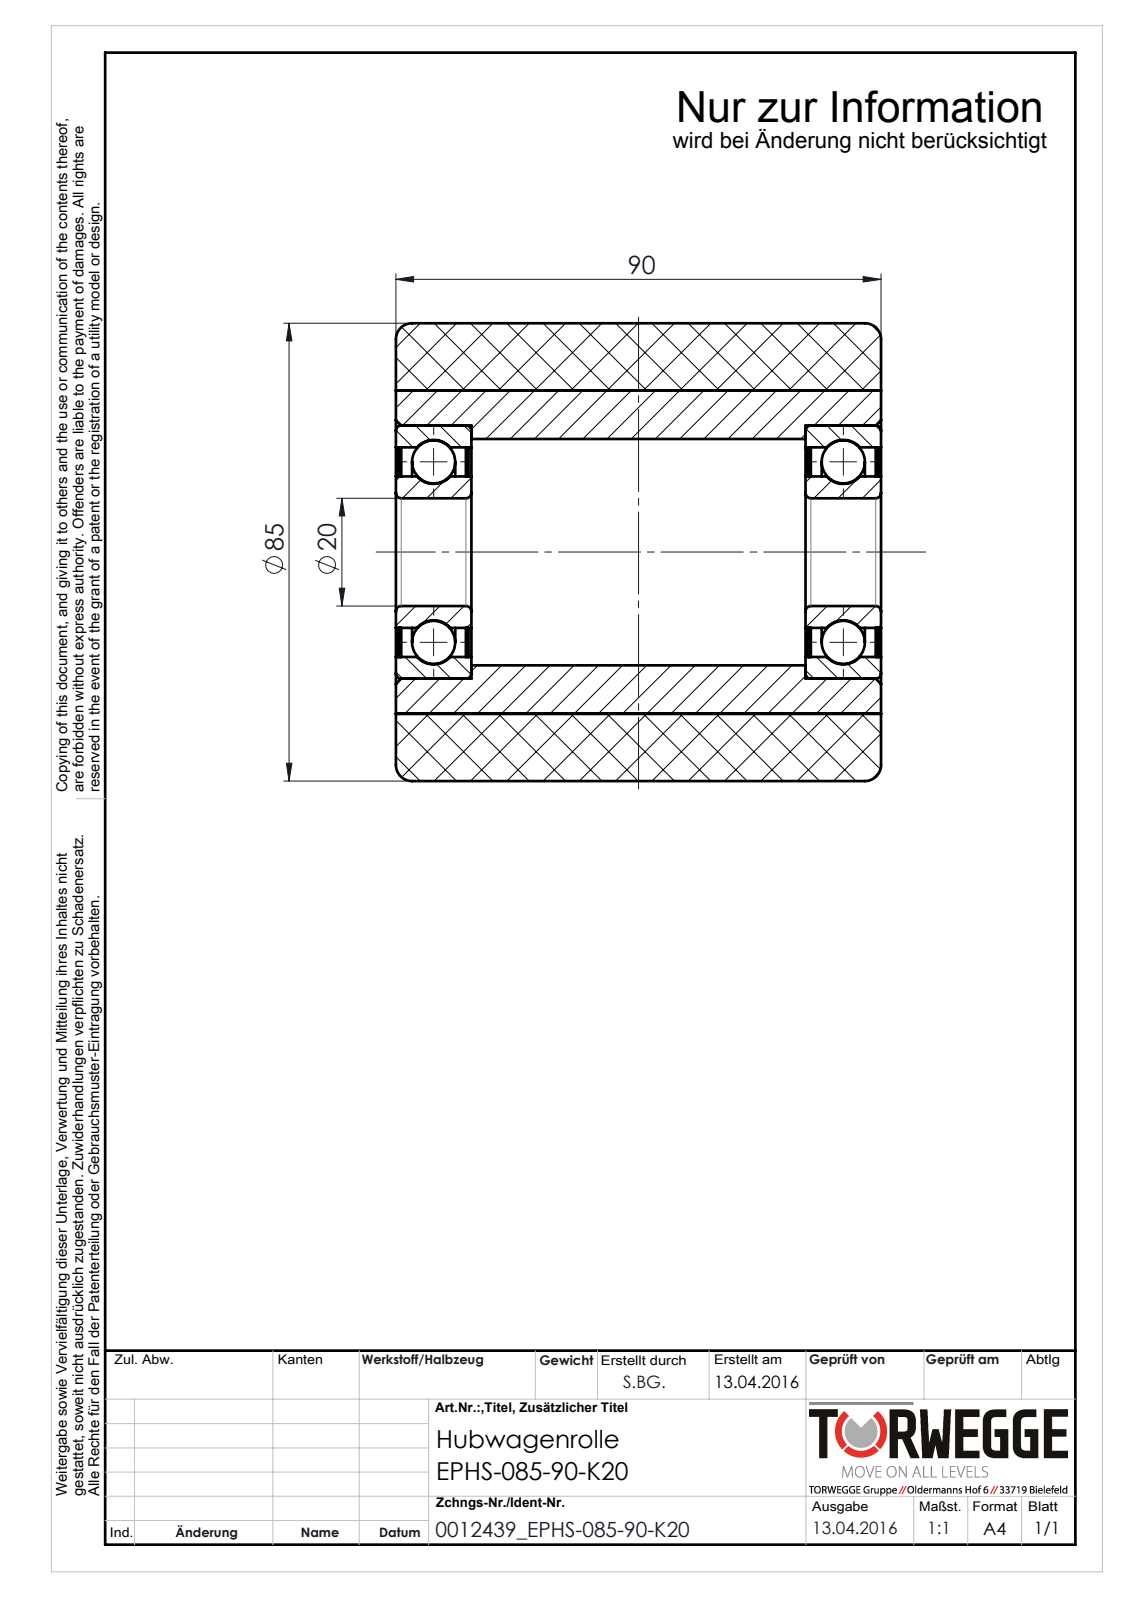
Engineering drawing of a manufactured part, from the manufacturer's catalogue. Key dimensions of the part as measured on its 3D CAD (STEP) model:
Part name (STEP PRODUCT): 0012439_EPHS-085-90-K20
STEP written by: SolidWorks 2016 (AUTOMOTIVE_DESIGN)
Units: millimetres
Bodies: 12 solids, 118 faces (22 planar, 52 cylindrical, 44 other)
Overall size (bounding box): 90 × 85 × 85
Volume: 407 948 mm³ · Surface area: 103 426 mm²
Round holes (diameter × count): ⌀20 ×1, ⌀28.1 ×1, ⌀38.9 ×1, ⌀42 ×1, ⌀47 ×1, ⌀60 ×1
Round bosses / shafts (diameter × count): ⌀85 ×1
Main face-to-face distances: 0.5, 76, 90, 13, 1, 13.5, 76.5, 75.5, 12.5, 14
